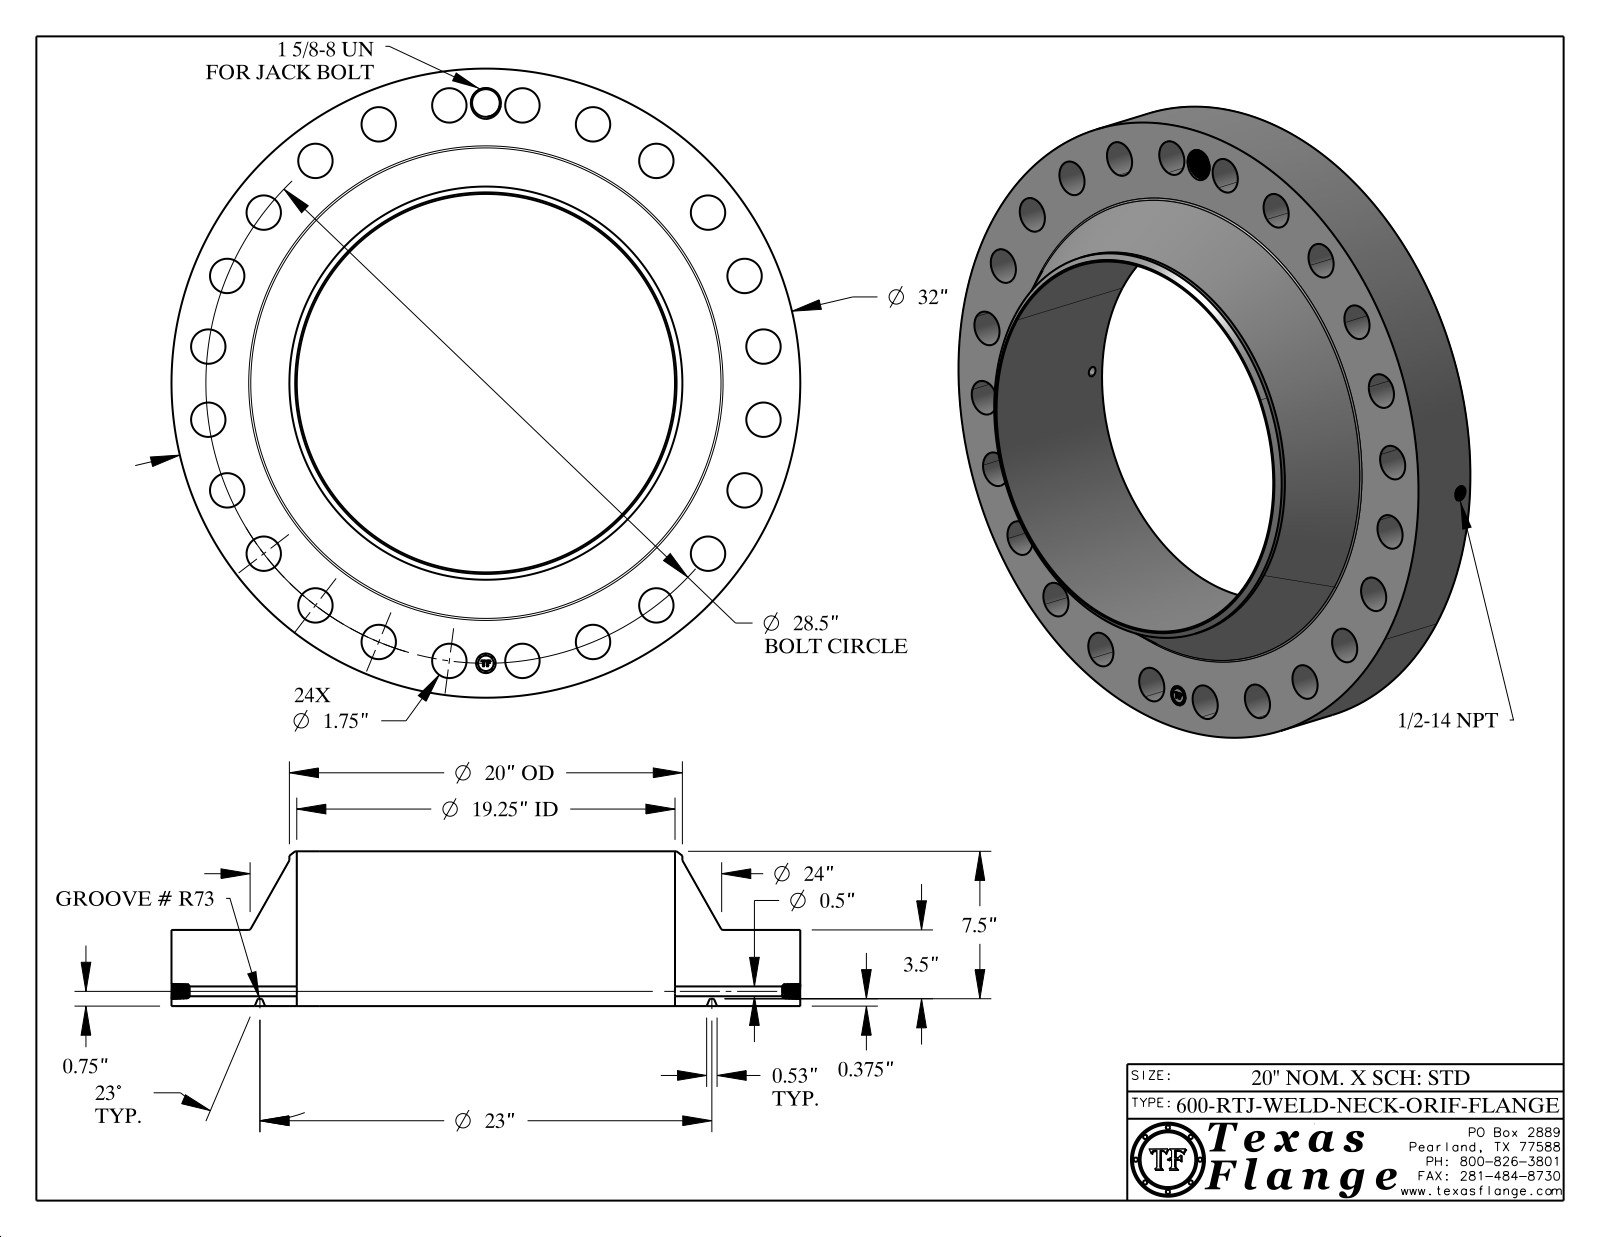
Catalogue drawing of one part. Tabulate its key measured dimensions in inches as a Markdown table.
| quantity | value |
| --- | --- |
| part name | 600-RTJ-WELD-NECK |
| STEP written by | CATIA V5 STEP AP214 (AUTOMOTIVE_DESIGN) |
| units | inches |
| bodies | 1 solid, 904 faces (370 planar, 155 cylindrical, 379 other) |
| overall size | 32 × 32 × 7.875 |
| volume | 2 072 in³ |
| surface area | 2 541 in² |
| round holes (diameter × count) | 1.75 × 24, 0.5 × 1, 0.672 × 1, 1 × 1, 1.409 × 1, 19.25 × 1 |
| round bosses / shafts (diameter × count) | 0.061 × 8, 32 × 1, 20 × 1, 0.788 × 1 |
| main face-to-face distances | 3.875, 0.375, 3.5, 7.875, 7.5, 4, 0.015, 3.86, 3.485, 4.015 |
| hole center spacings | 14.25, 17.35, 24.681, 28.256, 10.906, 3.72, 7.376, 20.152 |
